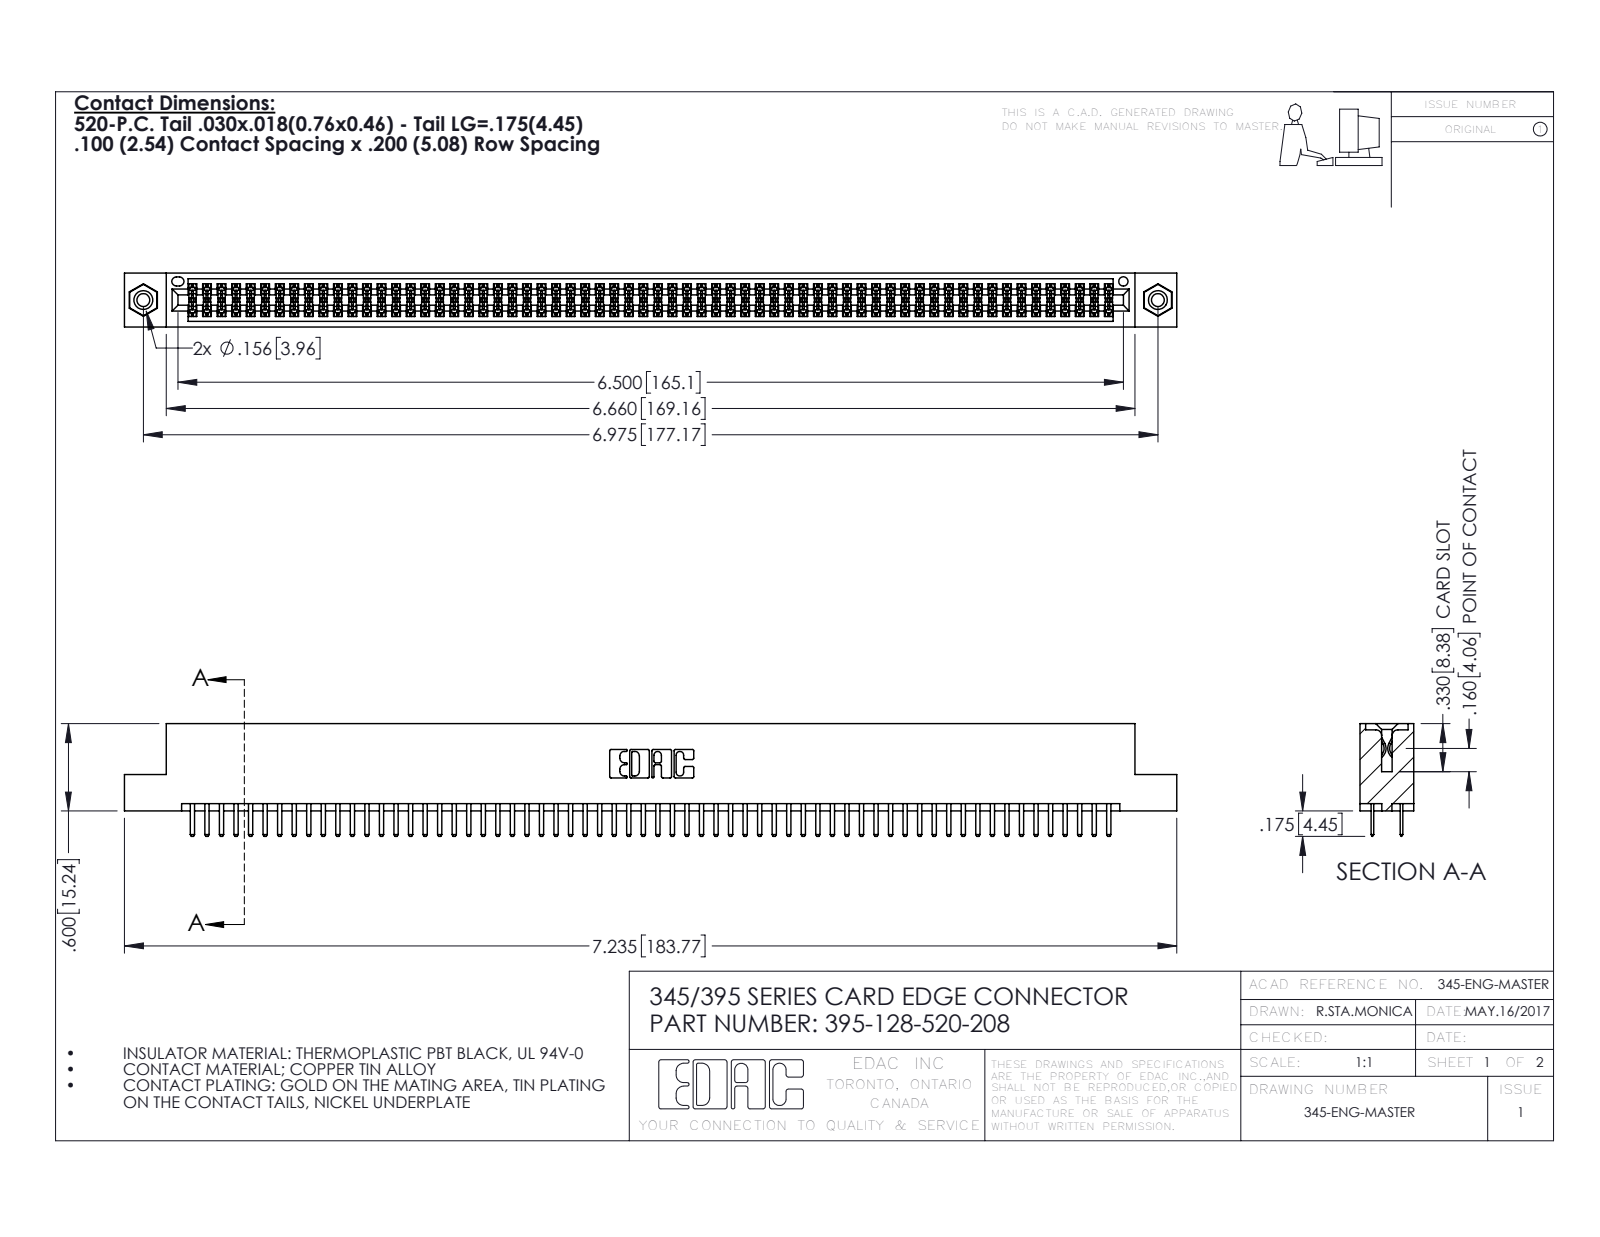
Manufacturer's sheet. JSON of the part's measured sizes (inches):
{"part_name": "345-250-001_345-250-003-102; 395-128-520-208; 345-292-001_345-293-120; 345 Part_Flush Mounting Lugs - 0.156 Dia-TI", "step_written_by": "SolidWorks 2016 (CONFIG_CONTROL_DESIGN)", "units": "inches", "bodies": {"solids": 131, "faces": 7098, "planar": 4592, "cylindrical": 2490, "other": 16}, "overall_size": [7.235, 0.775, 0.37], "volume_in3": 1.098, "surface_area_in2": 41.72, "round_holes": [[0.089, 2], [0.125, 2], [0.156, 2], [0.064, 1]], "round_bosses_or_shafts": [[0.155, 2]], "partial_cylinders_radius": [[0.006, 192], [0.01, 132], [0.01, 22], [0.007, 6], [0.031, 6], [0.026, 3], [0.014, 2], [0.019, 2]], "face_to_face_distances": [0.072, 0.298, 0.2, 0.37, 0.098, 0.272, 0.025, 0.225, 0.022, 0.072], "hole_center_spacings": [0.27, 6.739, 6.975]}
